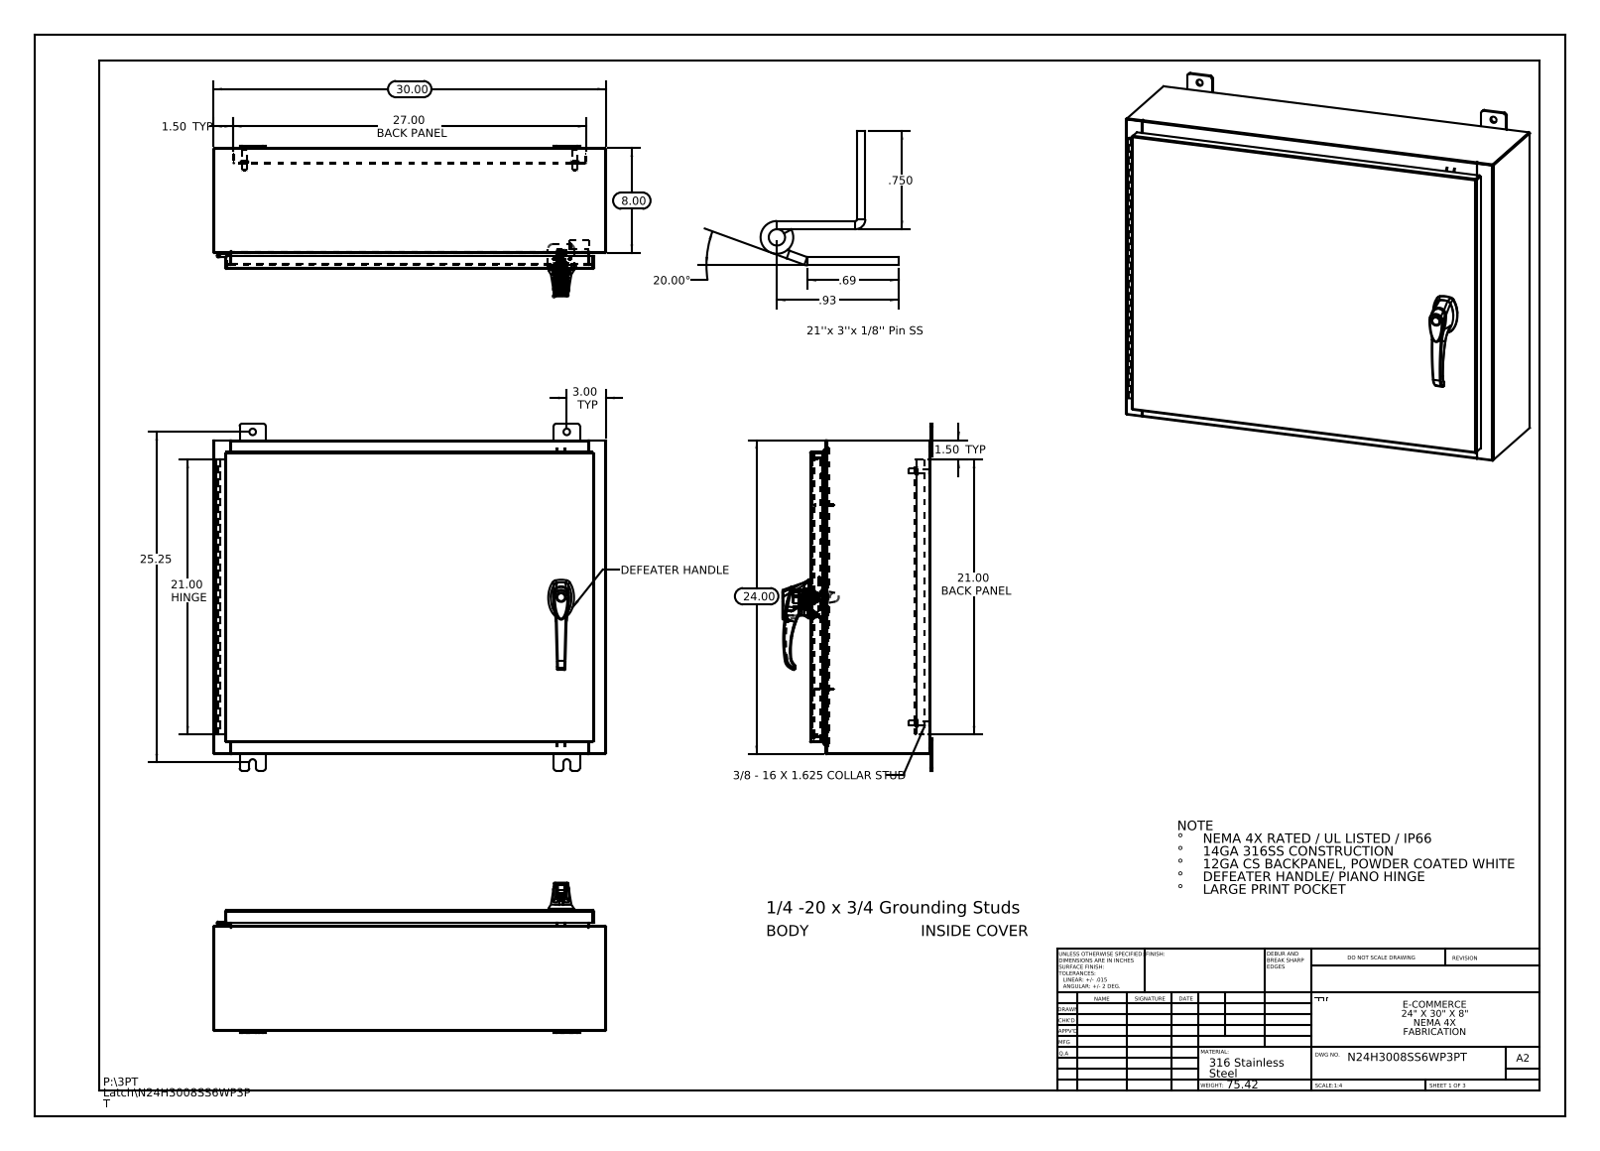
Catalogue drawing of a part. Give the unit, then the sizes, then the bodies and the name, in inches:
Units: inches
Overall size (bounding box): 30 × 26.5 × 11.495
Round holes (diameter × count): ⌀0.5 ×8, ⌀0.25 ×4, ⌀0.138 ×3, ⌀0.161 ×3, ⌀0.079 ×2, ⌀0.203 ×2, ⌀0.313 ×2, ⌀0.437 ×2, ⌀0.125 ×1, ⌀0.125 ×1, ⌀0.197 ×1, ⌀0.276 ×1
Round bosses / shafts (diameter × count): ⌀0.625 ×4, ⌀0.375 ×4, ⌀0.33 ×4, ⌀1.181 ×1, ⌀0.748 ×1, ⌀0.68 ×1, ⌀0.661 ×1, ⌀0.639 ×1
Partial cylindrical surfaces — rounded edges, fillets, slot ends (radius × count): R0.118 ×37, R0.006 ×33, R0.19 ×24, R0.013 ×22, R0.088 ×18, R0.039 ×15, R0.028 ×12, R0.008 ×6
Main face-to-face distances: 0.075, 9.126, 9.051, 9.201, 0.104, 1, 1.075, 8.051, 8.126, 1.179
Hole centre spacings: 7.68, 24, 0.295, 0.625, 0.841, 1.25, 1.313, 1.561
Volume: 267 in³ · Surface area: 6 596 in²
Bodies: 31 solids, 2412 faces (865 planar, 893 cylindrical, 654 other)
Part name (STEP PRODUCT): NMP-SS-RODGUIDES; N24H3008SS6WP3PT 263033_Industrilas; 26161102; N24H3008SS6WP3PT Defeater Handle - 3 - 2500-51 ZN (+8 more)
STEP written by: SolidWorks 2013 (CONFIG_CONTROL_DESIGN)
